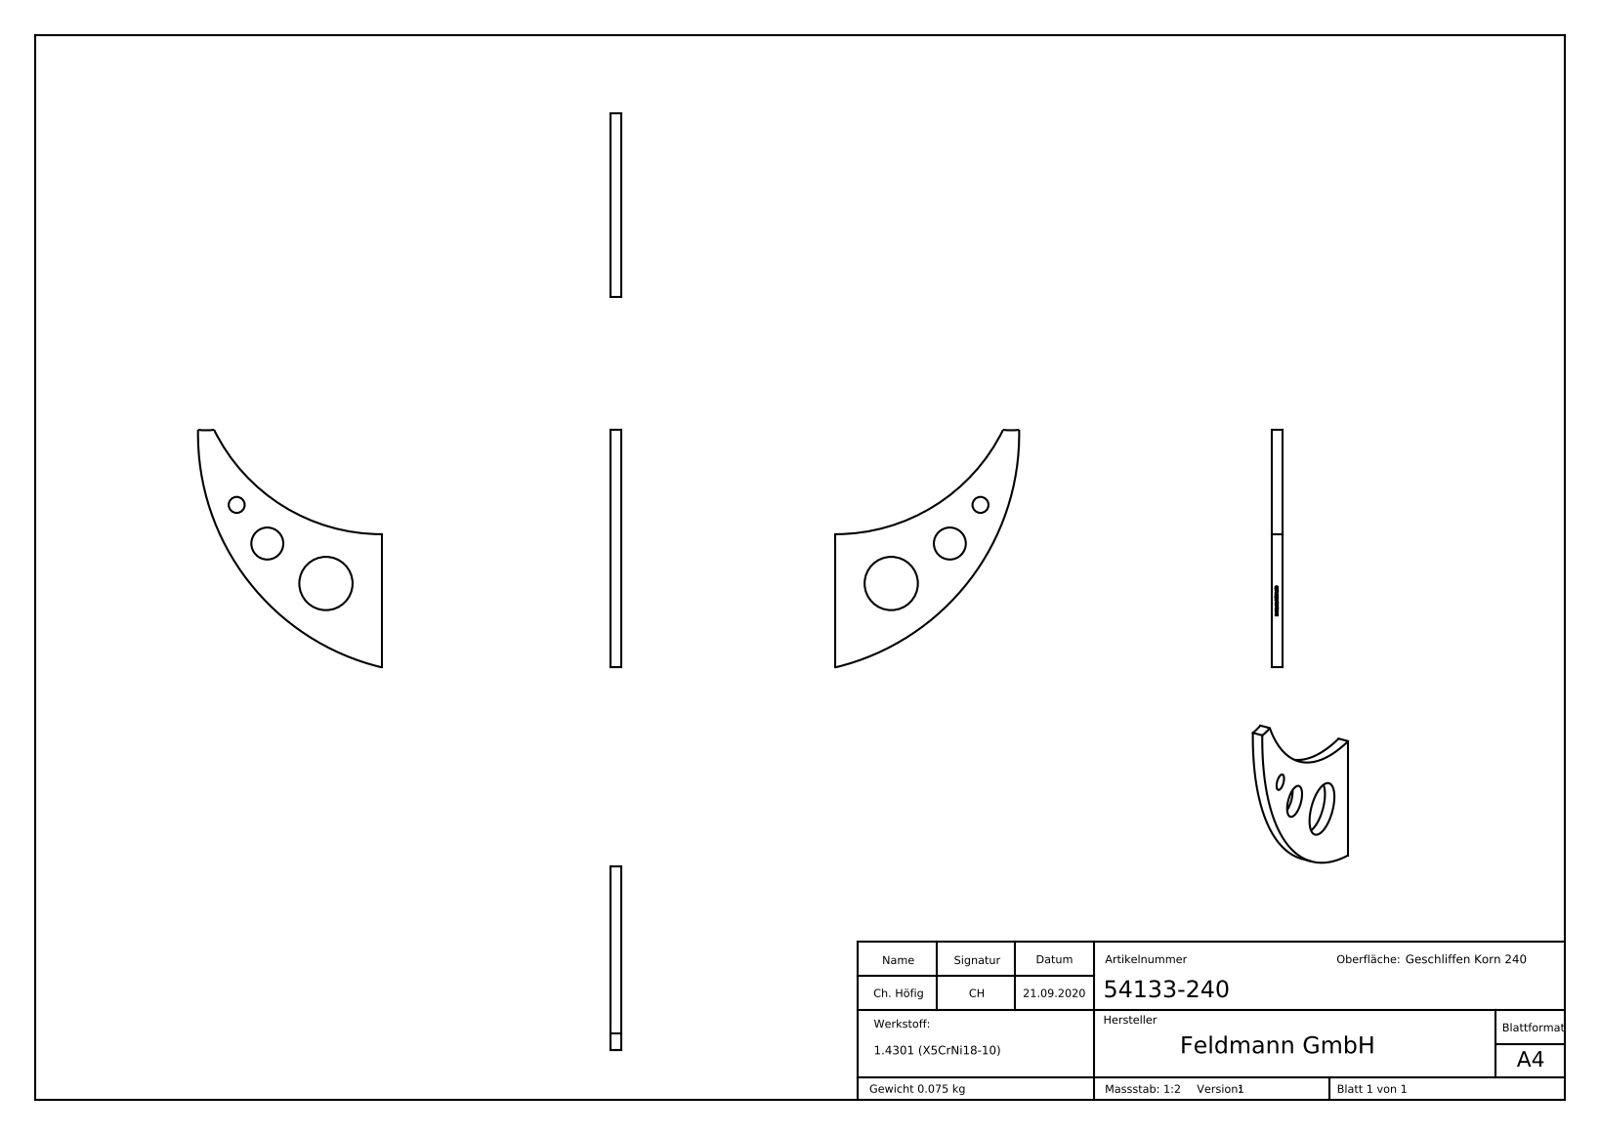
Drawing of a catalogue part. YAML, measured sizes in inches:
part_name: "54133-240"
step_written_by: "SolidWorks 2018 (CONFIG_CONTROL_DESIGN)"
units: inches
bodies: {solids: 1, faces: 242, planar: 134, cylindrical: 9, other: 99}
overall_size: [3.512, 2.717, 0.157]
volume: 0.581
surface_area: 9.717
round_holes:
  - {diameter: 0.236, count: 1}
  - {diameter: 0.472, count: 1}
  - {diameter: 0.787, count: 1}
partial_cylinders:
  - {radius: 0.835, count: 1}
  - {radius: 2.756, count: 1}
  - {radius: 3.543, count: 1}
face_to_face_distances: [0.157, 0.079, 0.048, 0.07, 0.021, 0.033, 0.016, 0.111, 0.103, 0.017]
hole_center_spacings: [0.729, 1.048, 1.757]
